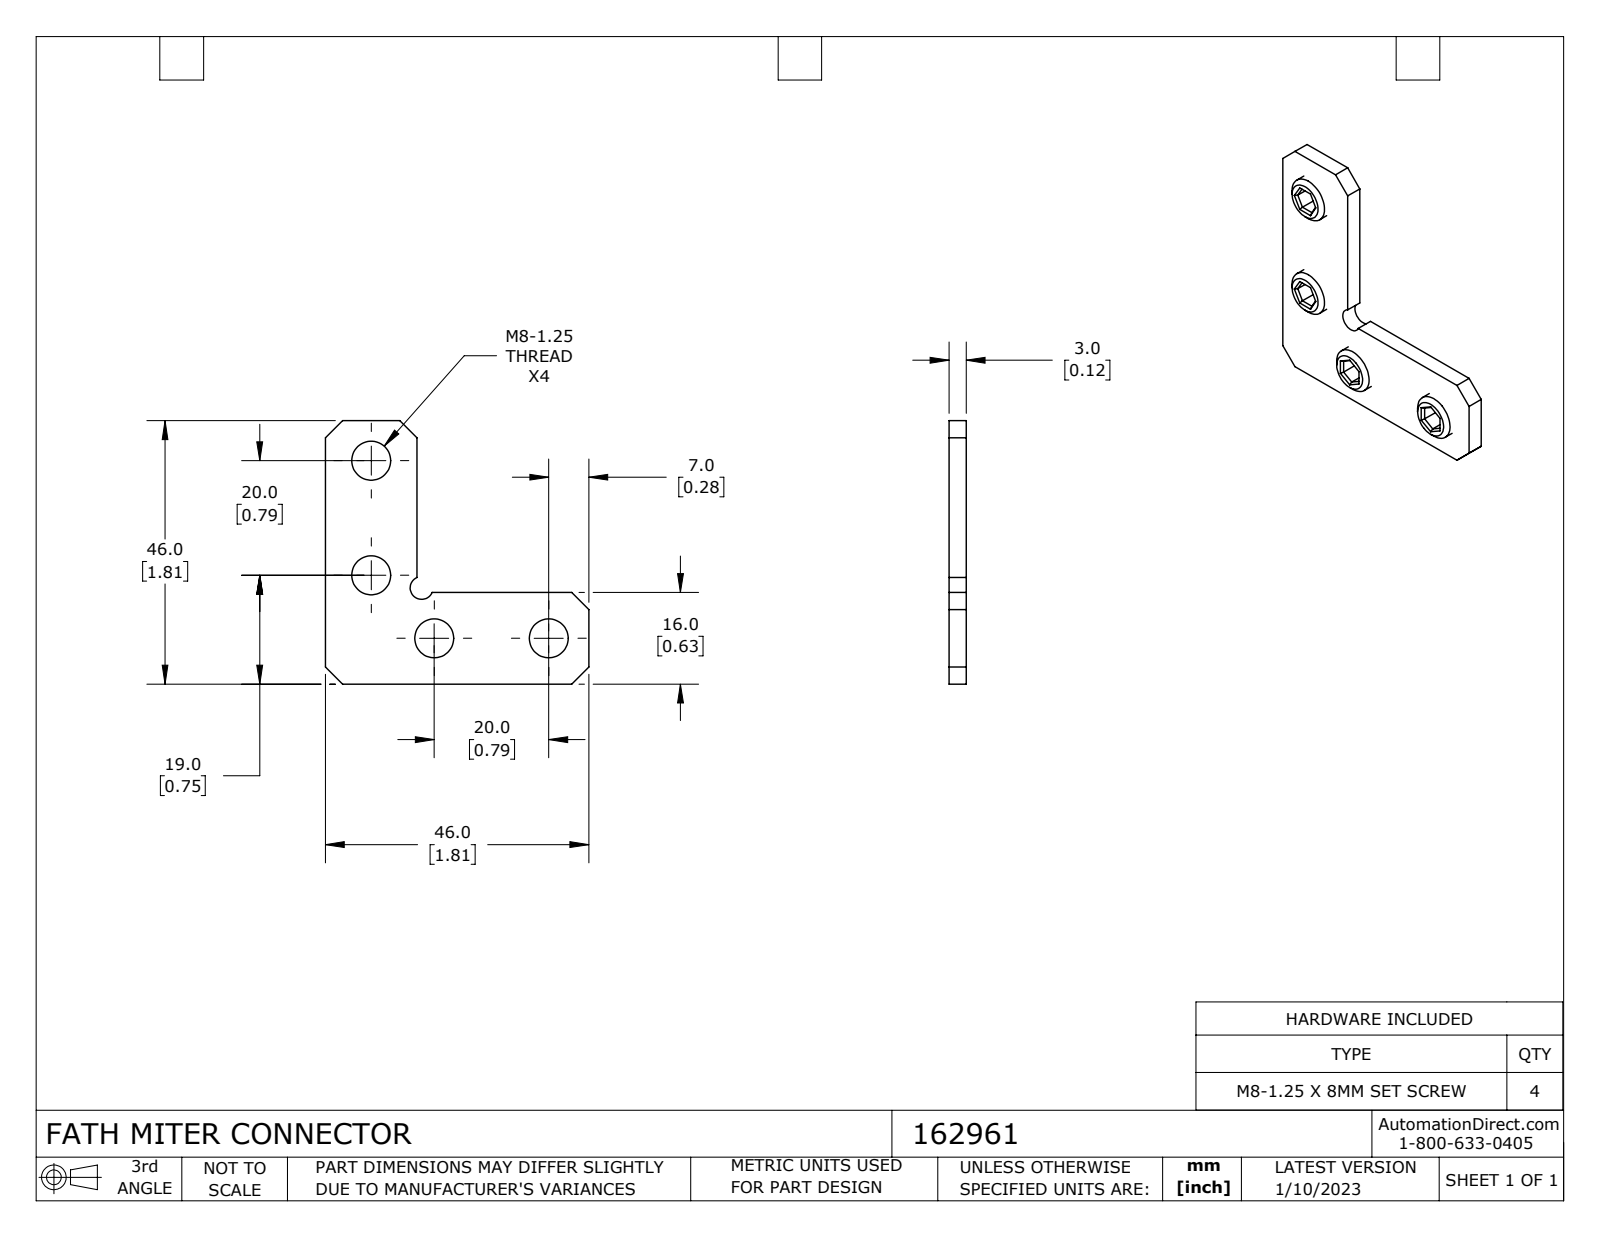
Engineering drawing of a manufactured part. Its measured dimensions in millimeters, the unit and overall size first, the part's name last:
Units: millimetres
Overall size (bounding box): 46 × 46 × 8
Round holes (diameter × count): ⌀6.8 ×4
Round bosses / shafts (diameter × count): ⌀8 ×4
Partial cylindrical surfaces — rounded edges, fillets, slot ends (radius × count): R2 ×1
Main face-to-face distances: 3, 16, 2.5, 5.5, 4, 10, 46, 30, 8, 21
Hole centre spacings: 20, 32.9, 15.6, 43.8
Volume: 4 310 mm³ · Surface area: 4 250 mm²
Bodies: 5 solids, 135 faces (93 planar, 18 cylindrical, 24 other)
Part name (STEP PRODUCT): 162961
STEP written by: SolidWorks 2021 (CONFIG_CONTROL_DESIGN)
